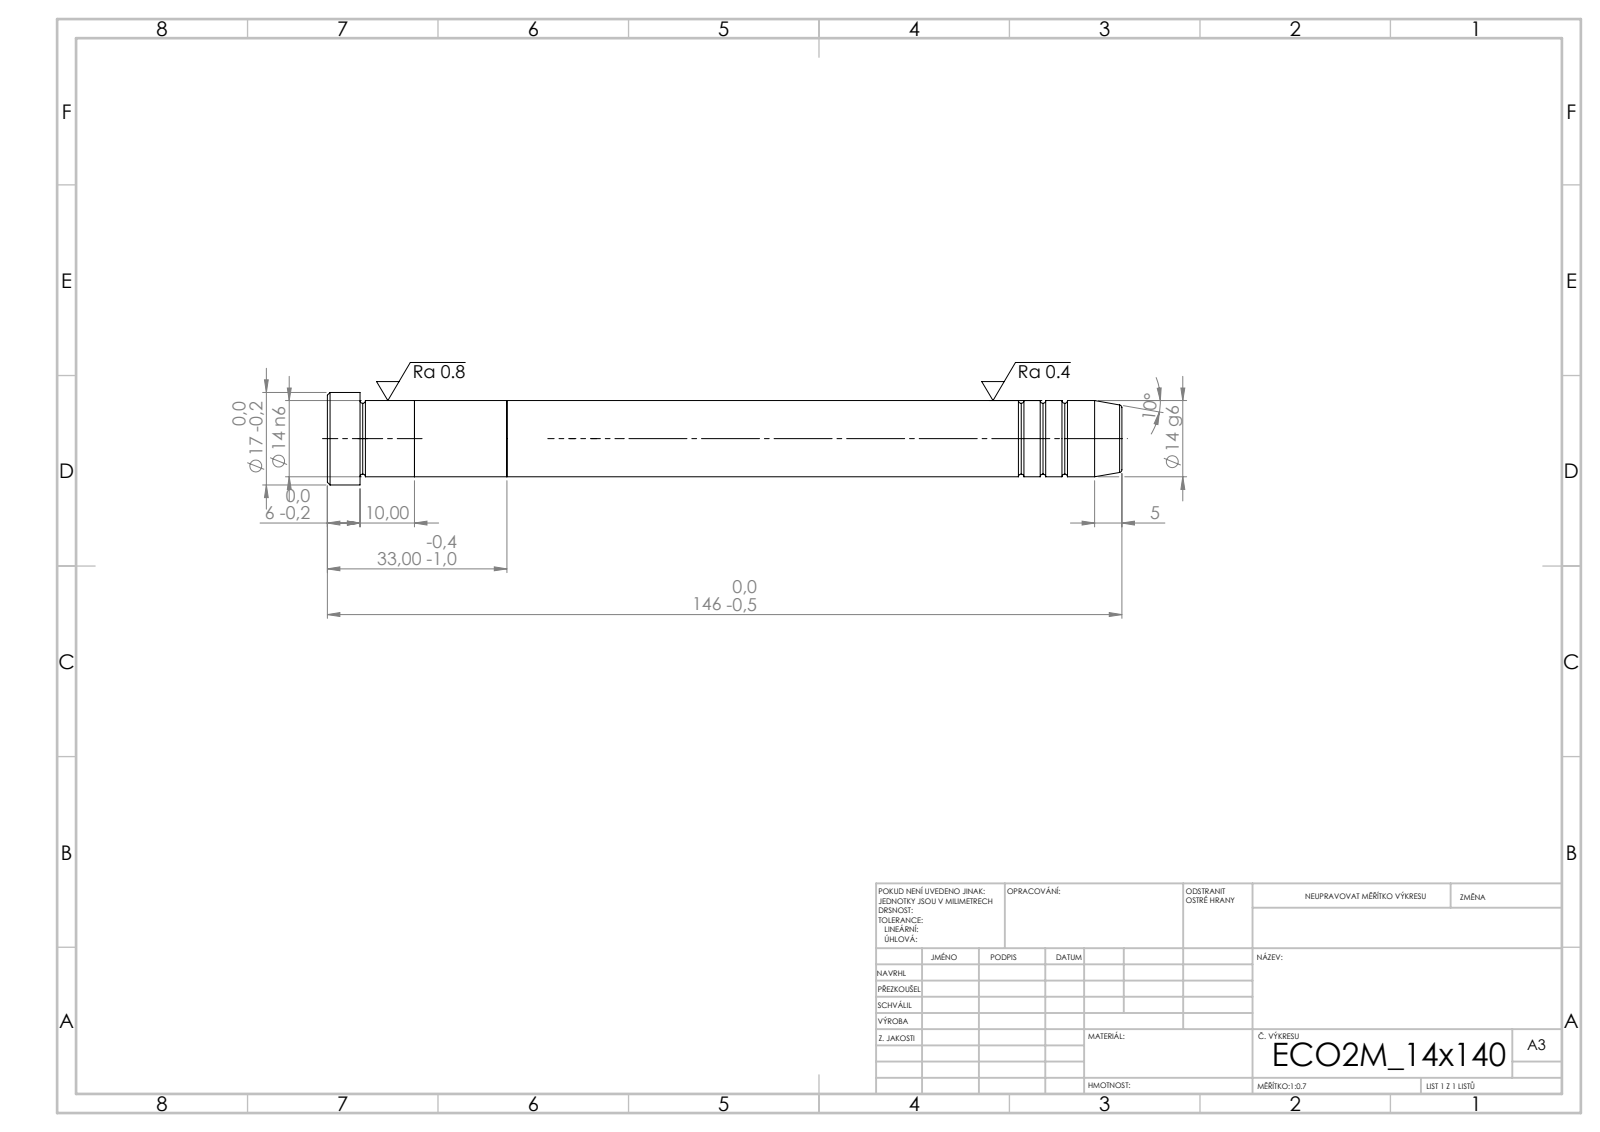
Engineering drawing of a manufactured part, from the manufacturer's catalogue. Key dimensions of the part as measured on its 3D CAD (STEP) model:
STEP written by: SolidWorks 2019 (CONFIG_CONTROL_DESIGN)
Units: millimetres
Bodies: 3 solids, 43 faces (7 planar, 14 cylindrical, 22 other)
Overall size (bounding box): 146 × 17 × 17
Volume: 22 745 mm³ · Surface area: 7 567 mm²
Round bosses / shafts (diameter × count): ⌀17 ×1, ⌀14 ×1
Main face-to-face distances: 17, 33, 16, 113, 130, 146, 140, 27, 10, 6
